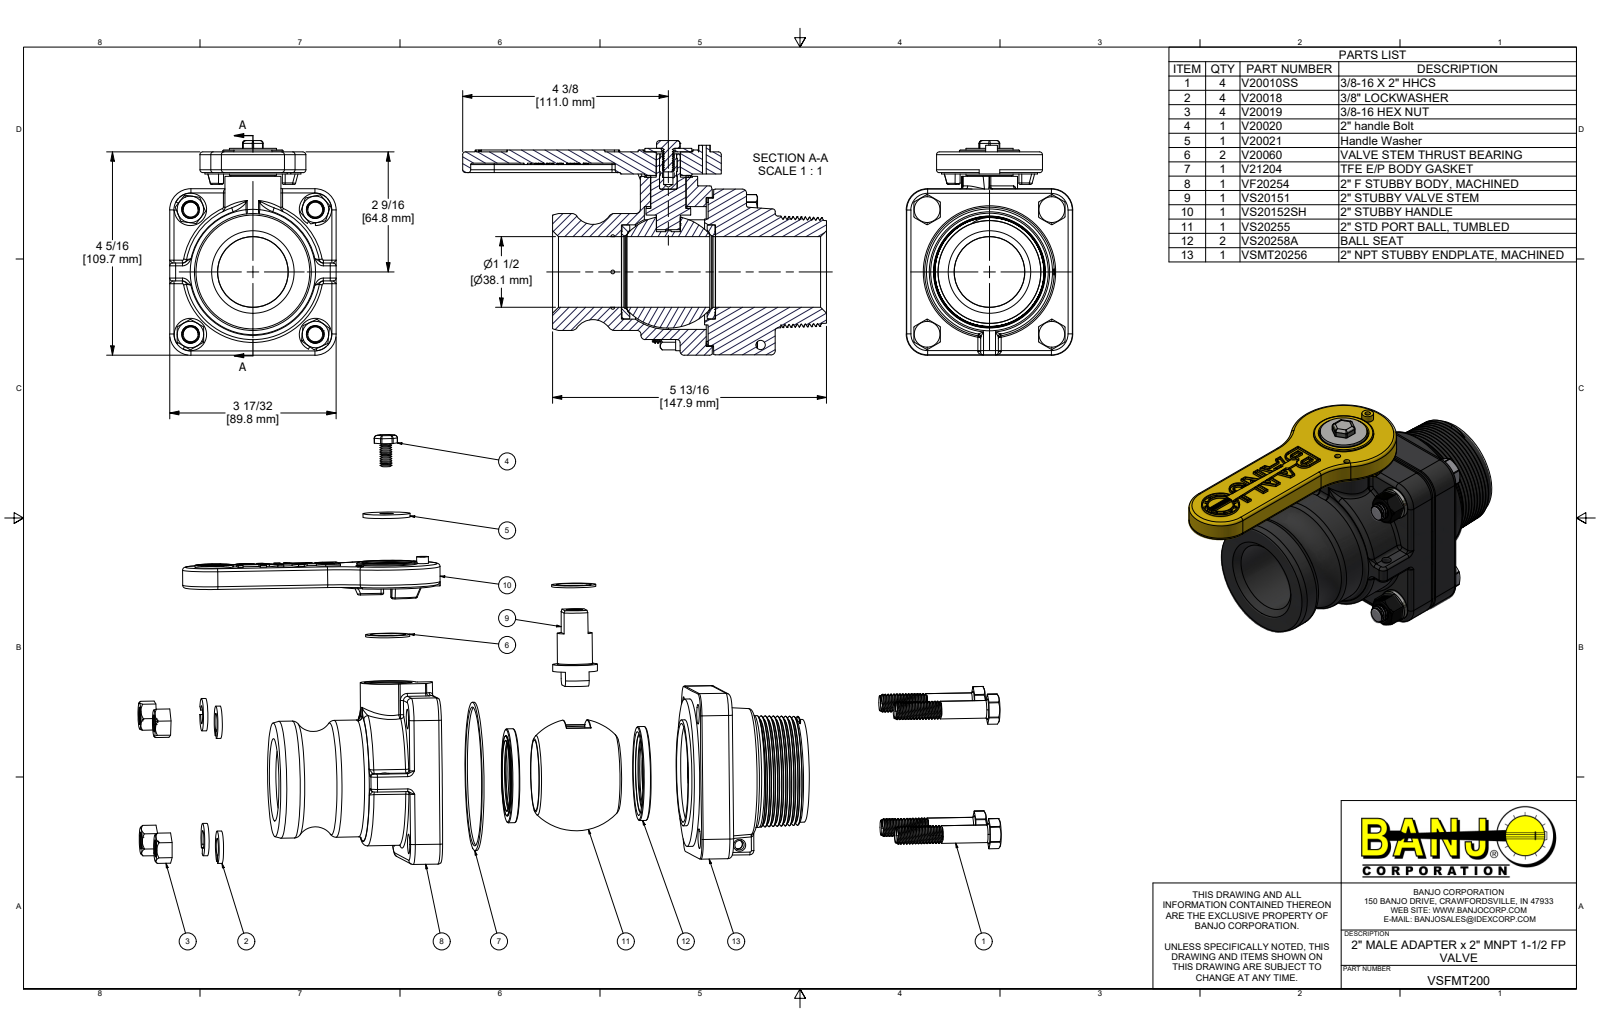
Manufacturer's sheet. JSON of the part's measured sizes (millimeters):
{"part_name": "VXF20254; VF20254; VXMT20256; VSMT20256 (+8 more)", "step_written_by": "Autodesk Inventor 2016 (AUTOMOTIVE_DESIGN)", "units": "millimeters", "bodies": {"solids": 25, "faces": 2449, "planar": 881, "cylindrical": 612, "other": 956}, "overall_size": [196.38, 116.1, 90.42], "volume_mm3": 534320, "surface_area_mm2": 154395, "round_holes": [[10.31, 8], [9.52, 5], [7.81, 4], [9.78, 4], [5.08, 3], [2.03, 2], [3.3, 2], [3, 1], [4.98, 1], [7.14, 1], [8.92, 1], [13.83, 1]], "round_bosses_or_shafts": [[8.24, 60], [17.46, 4], [9.52, 4], [80.01, 1], [79.5, 1], [63.04, 1], [60.32, 1], [57.15, 1]], "partial_cylinders_radius": [[1.52, 32], [2.29, 22], [0.76, 15], [3.17, 8], [4.12, 8], [8.12, 4], [11.89, 4], [11.91, 4]], "face_to_face_distances": [90.42, 20.7, 35.85, 15.15, 1.02, 6.86, 17.46, 2.31, 18.39, 12.7], "hole_center_spacings": [67.39, 47.56, 47.74, 67.26, 67.52, 95.3, 40.46, 46.12]}
